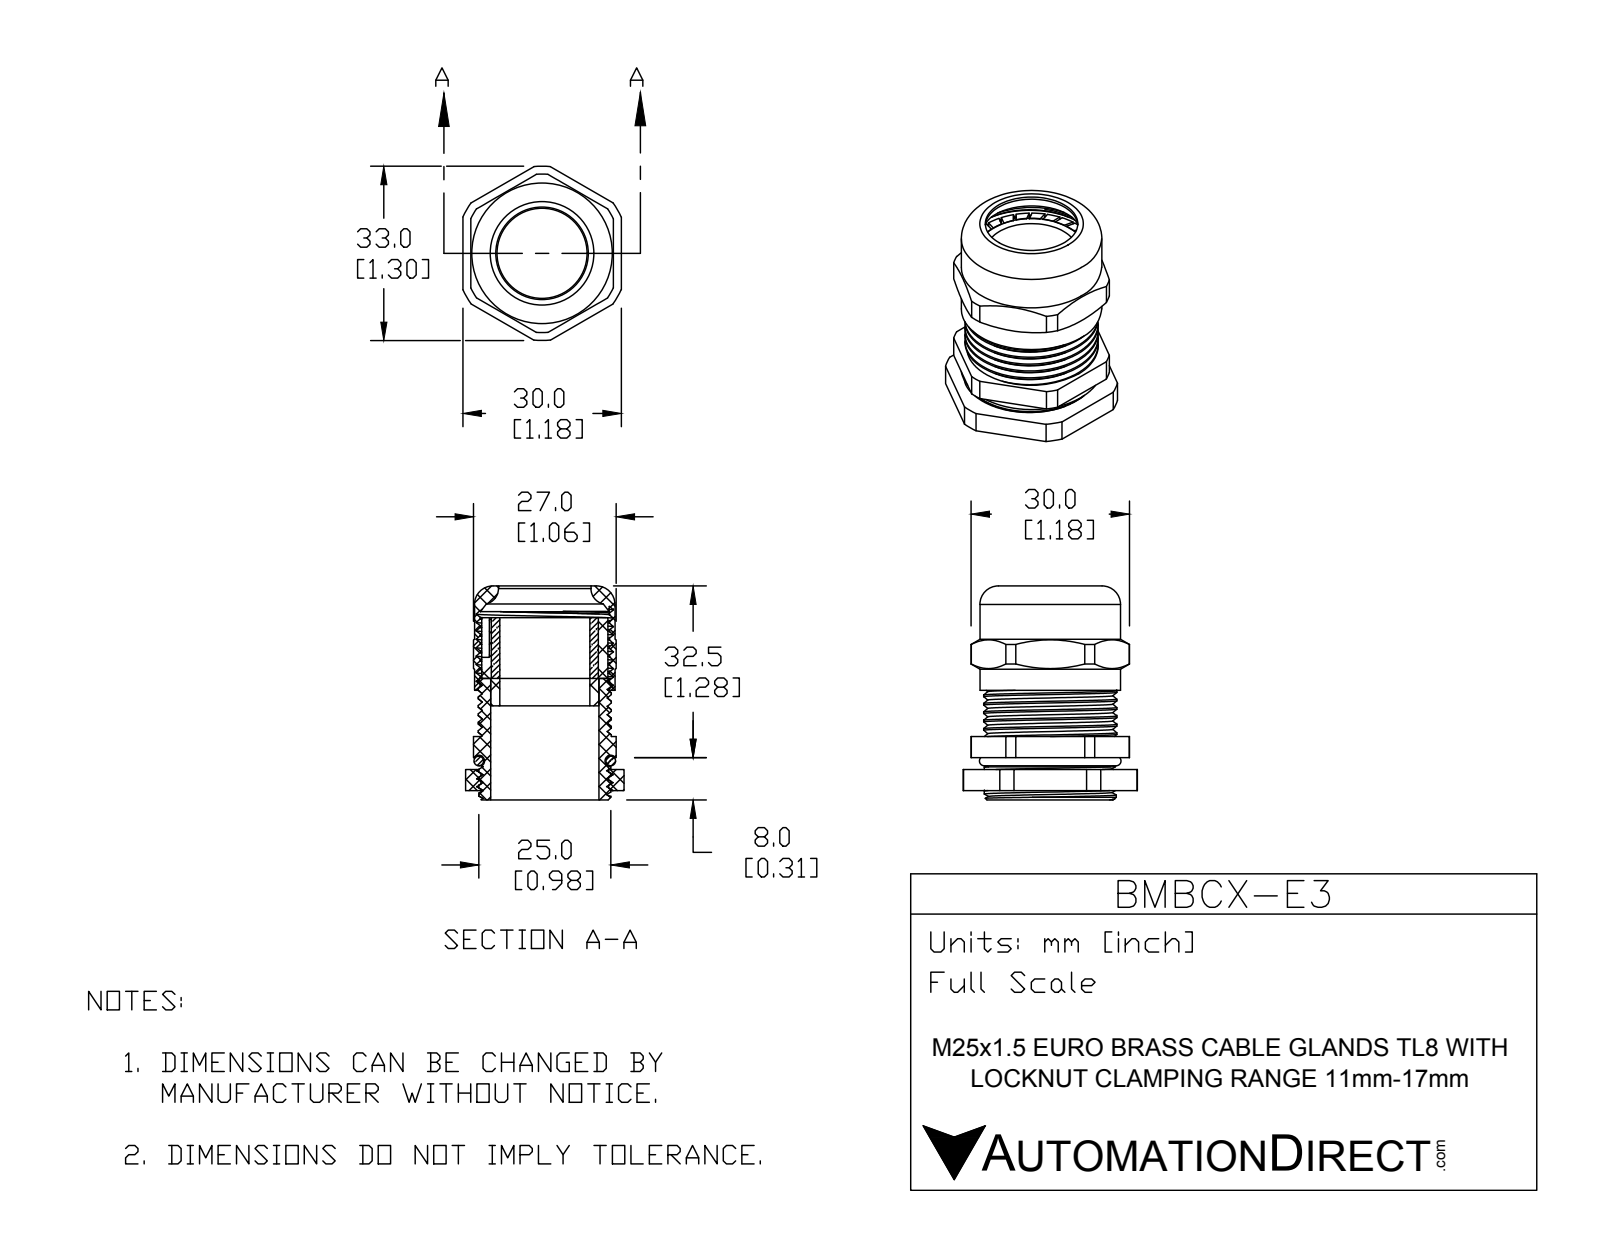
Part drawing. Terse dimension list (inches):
name: BMBCX-E3
written by: SolidWorks 2015 (CONFIG_CONTROL_DESIGN)
unit: in
bodies: 6 solids, 256 faces (133 planar, 91 cylindrical, 32 other)
size: 1.594 × 1.299 × 1.181
volume: 0.625 in³; area: 24.18 in²
holes: 1× ⌀0.671, 1× ⌀0.689, 1× ⌀0.797, 1× ⌀0.807, 1× ⌀0.952, 1× ⌀0.962
bosses: 1× ⌀1.047, 1× ⌀0.992, 1× ⌀0.984, 1× ⌀0.941
rounds: 1× R0.591, 1× R0.65
face distances: 1.122, 0.157, 1.063, 0.02, 0.059, 0.836, 0.678, 0.245, 1.289, 1.131
